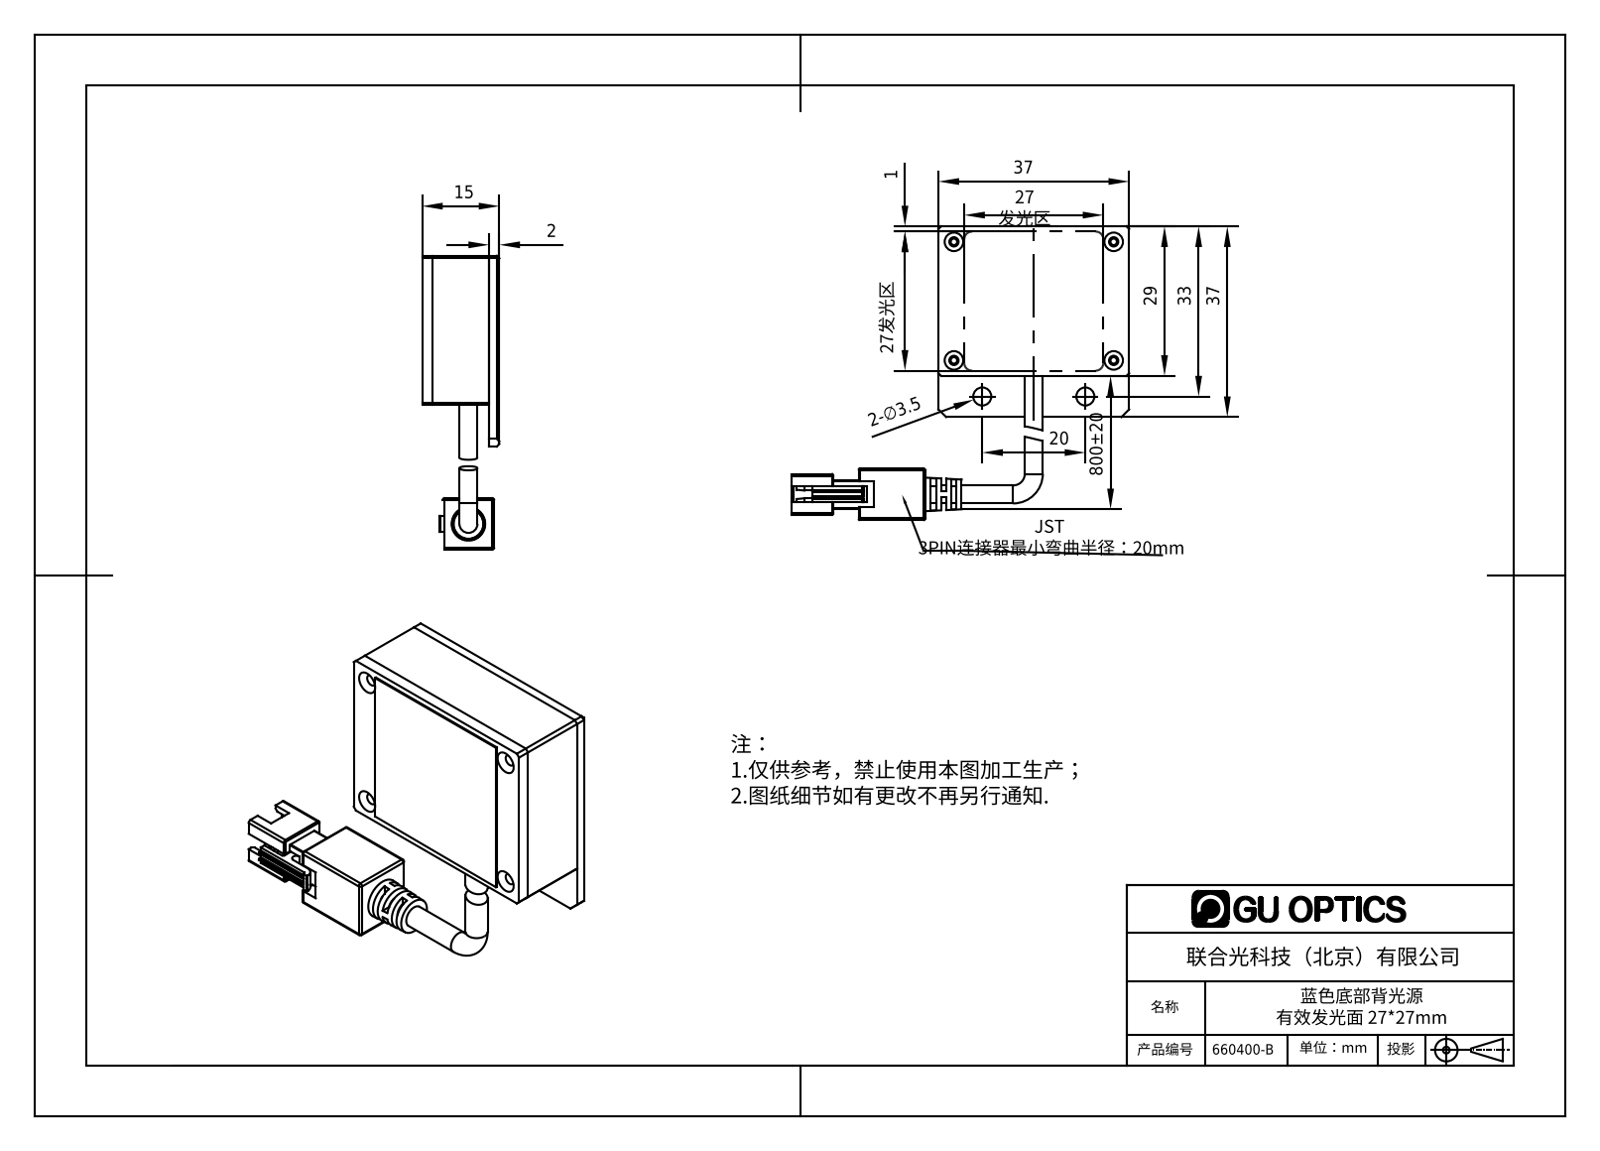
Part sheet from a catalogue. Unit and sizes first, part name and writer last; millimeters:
Units: millimetres
Overall size (bounding box): 65.5 × 57 × 15.2
Round holes (diameter × count): ⌀1.25 ×4, ⌀1.6 ×4, ⌀1.8 ×4, ⌀2 ×4, ⌀2.4 ×4, ⌀3.5 ×2
Round bosses / shafts (diameter × count): ⌀3.5 ×2
Partial cylindrical surfaces — rounded edges, fillets, slot ends (radius × count): R0.1 ×15, R0.2 ×13, R0.4 ×12, R1 ×4, R1.5 ×4, R0.75 ×2, R0.8 ×2, R0.3 ×1
Main face-to-face distances: 2, 1, 11, 13, 2.3, 10.7, 1.3, 28, 2.2, 15.2
Hole centre spacings: 8.9, 23, 26.44, 30.5, 31, 38.6, 39.37, 20
Volume: 11 682 mm³ · Surface area: 12 966 mm²
Bodies: 6 solids, 616 faces (375 planar, 122 cylindrical, 119 other)
Part name (STEP PRODUCT): 660400-B
STEP written by: SolidWorks 2016 (AUTOMOTIVE_DESIGN)
